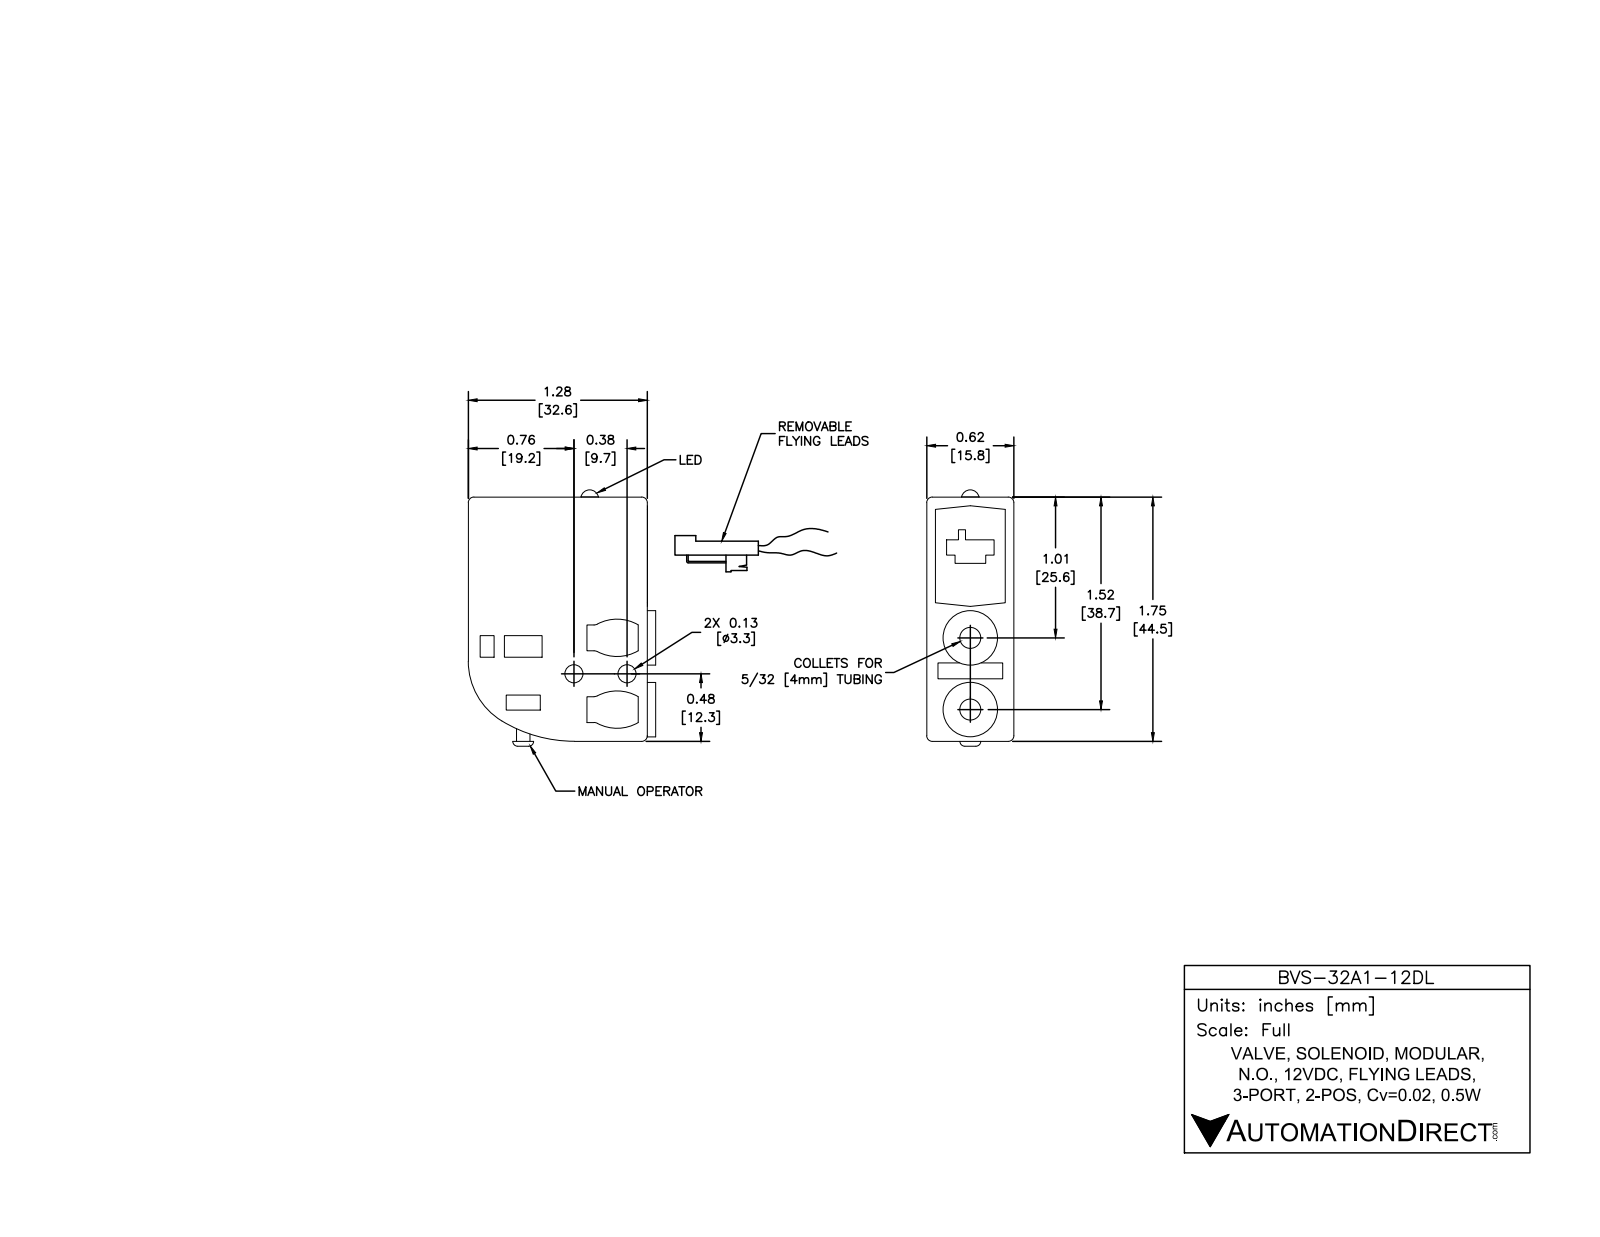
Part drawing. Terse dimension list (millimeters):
name: BVS-32A1-12DL
written by: SolidWorks 2016 (AUTOMOTIVE_DESIGN)
unit: mm
bodies: 1 solid, 149 faces (83 planar, 54 cylindrical, 12 other)
size: 46.7 × 45.4 × 15.7
volume: 20 630 mm³; area: 6 690 mm²
holes: 2× ⌀3.3, 2× ⌀3.8, 2× ⌀6.4, 1× ⌀1.3
bosses: 6× ⌀1.5, 2× ⌀9.9, 1× ⌀2.5
rounds: 4× R1.3, 4× R7.6, 3× R1, 1× R12.7, 1× R25.4
face distances: 15.7, 2.5, 32.8, 13.2, 32.8, 44.5, 25.4, 3.8, 1.5, 34.3
hole spacings: 1.5, 9.7, 11.4, 13
